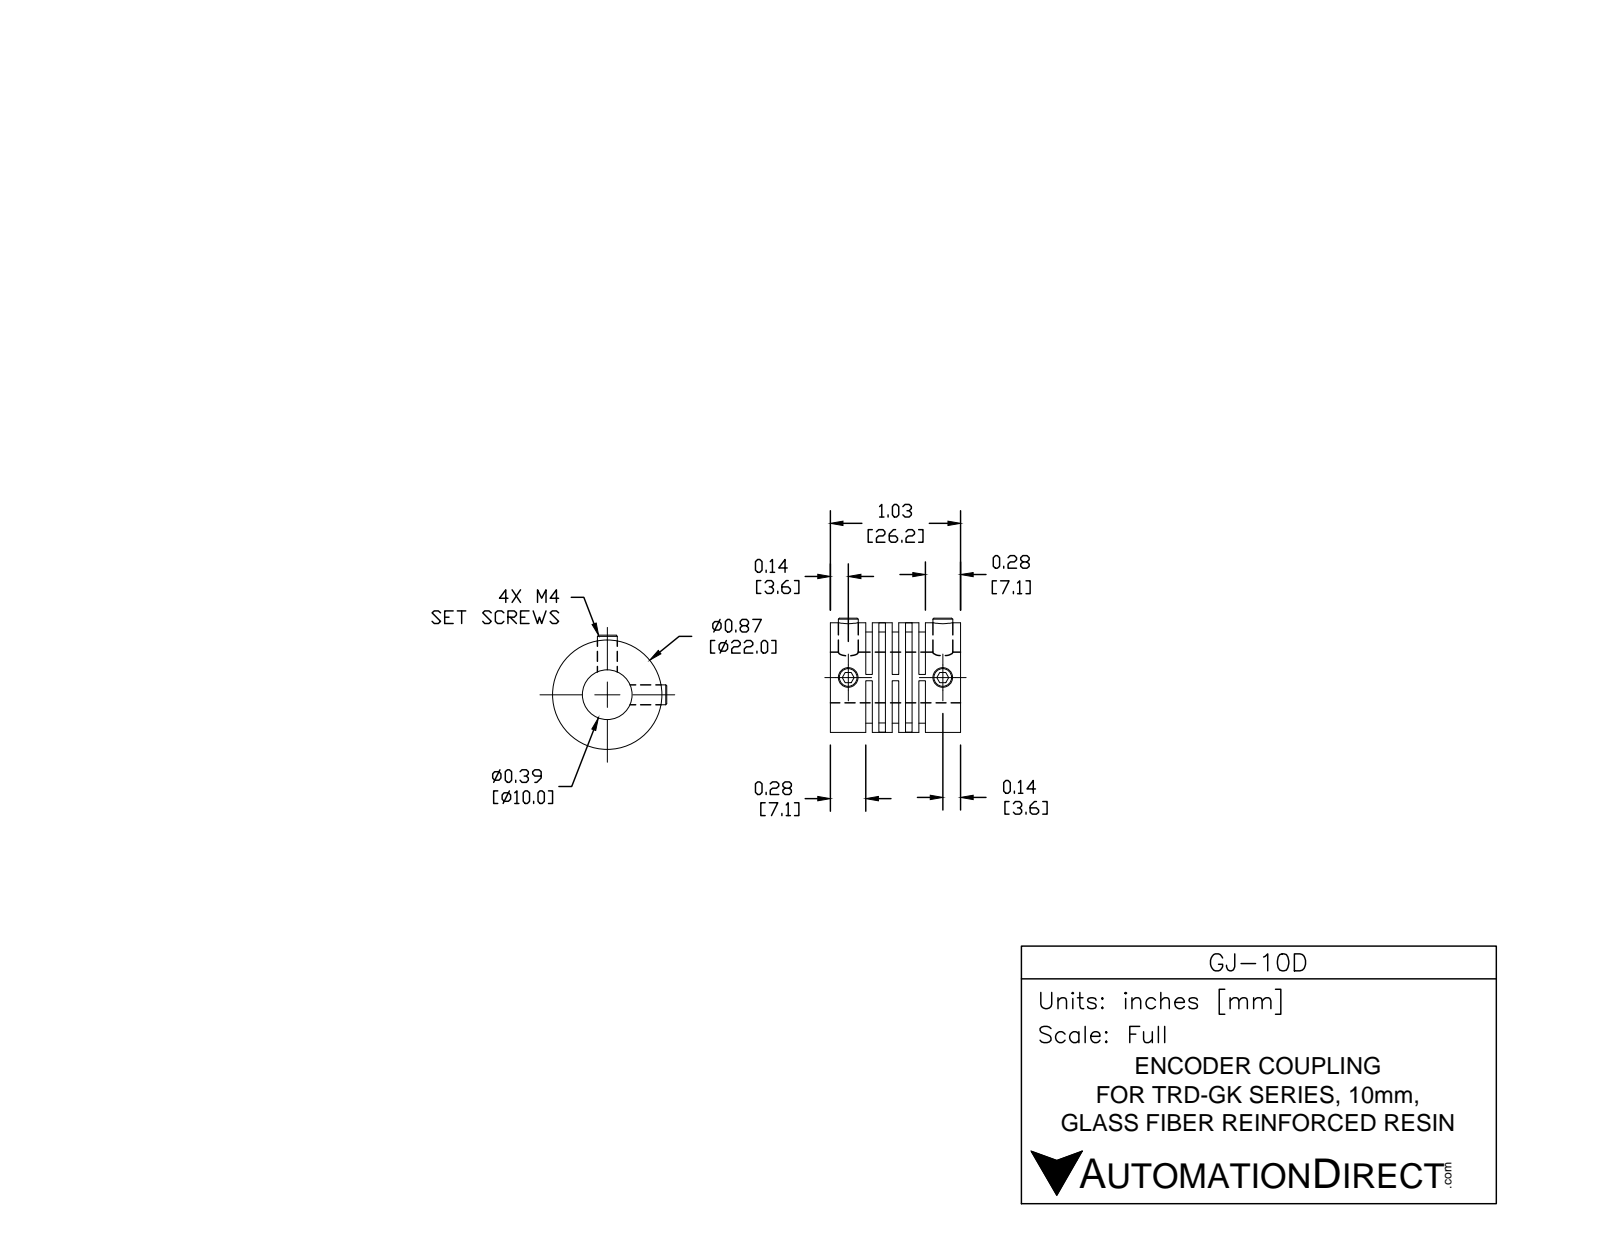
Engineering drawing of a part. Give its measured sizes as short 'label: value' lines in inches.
name: GJ-10D
written by: SolidWorks 2016 (AUTOMOTIVE_DESIGN)
unit: in
bodies: 1 solid, 130 faces (78 planar, 20 cylindrical, 32 other)
size: 1.024 × 0.866 × 0.866
volume: 0.369 in³; area: 8.964 in²
holes: 4× ⌀0.142, 1× ⌀0.394
bosses: 1× ⌀0.866
face distances: 0.102, 0.205, 0.047, 0.15, 0.307, 0.055, 0.252, 0.157, 0.283, 0.331
hole spacings: 0.74
